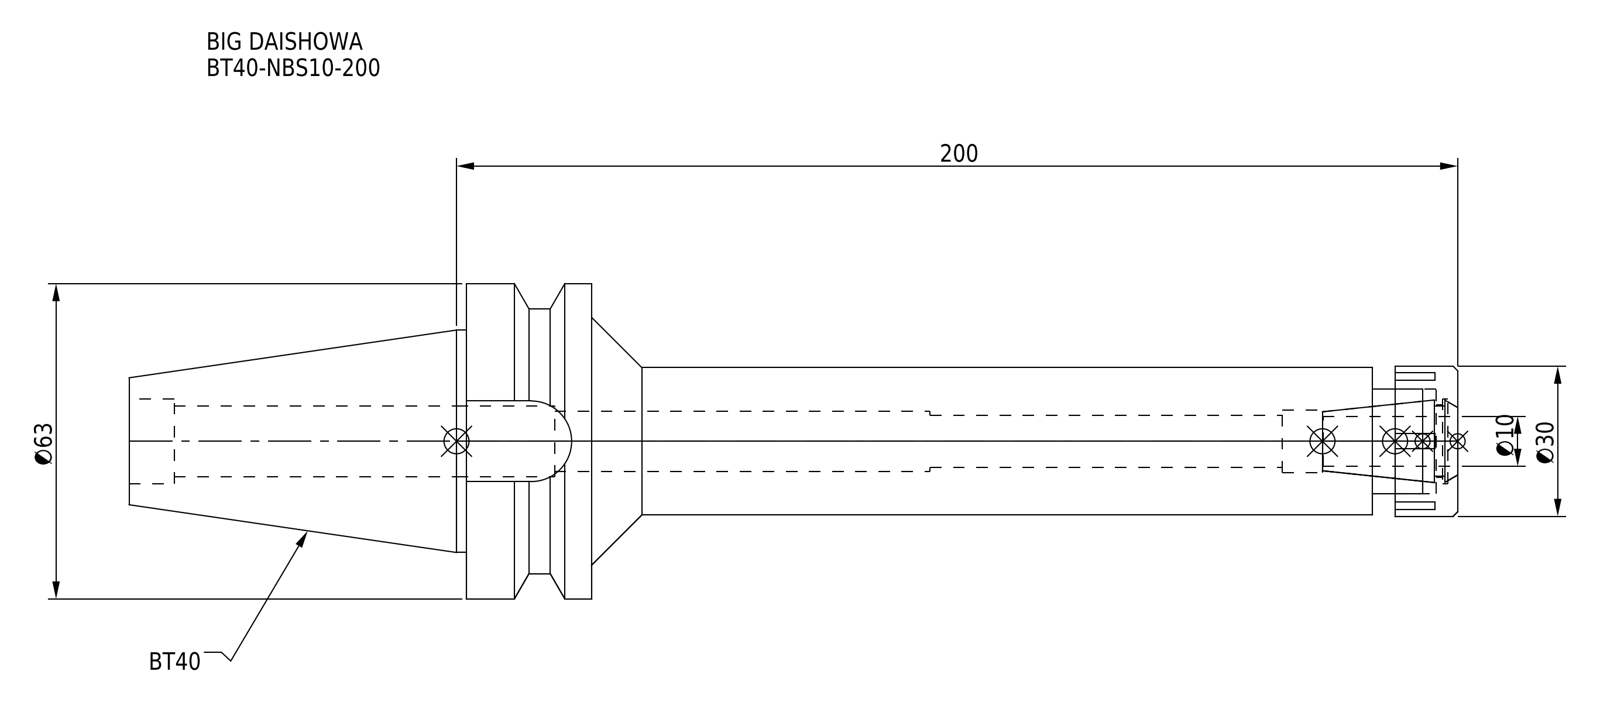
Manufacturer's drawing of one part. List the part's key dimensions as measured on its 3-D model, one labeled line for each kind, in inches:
Part name (STEP PRODUCT): BT40-NBS10-200.stp; NBN10_1.stp; BT40-NBS10-200-FreeParts; BT40-NBS10-200 (+3 more)
STEP written by: SolidWorks 2019 (CONFIG_CONTROL_DESIGN)
Units: inches
Bodies: 2 solids, 93 faces (45 planar, 34 cylindrical, 14 other)
Overall size (bounding box): 10.449 × 2.48 × 2.48
Volume: 13.57 in³ · Surface area: 72.31 in²
Round holes (diameter × count): ⌀0.409 ×1, ⌀0.472 ×1, ⌀0.492 ×1, ⌀0.559 ×1, ⌀0.571 ×1, ⌀0.669 ×1, ⌀0.827 ×1
Round bosses / shafts (diameter × count): ⌀2.48 ×1, ⌀2.087 ×1, ⌀1.75 ×1, ⌀1.181 ×1, ⌀1.161 ×1
Partial cylindrical surfaces — rounded edges, fillets, slot ends (radius × count): R0.317 ×1
Main face-to-face distances: 0.984, 6.811, 7.795, 0.177, 0.492, 0.669, 6.142, 7.126, 6.319, 7.303
